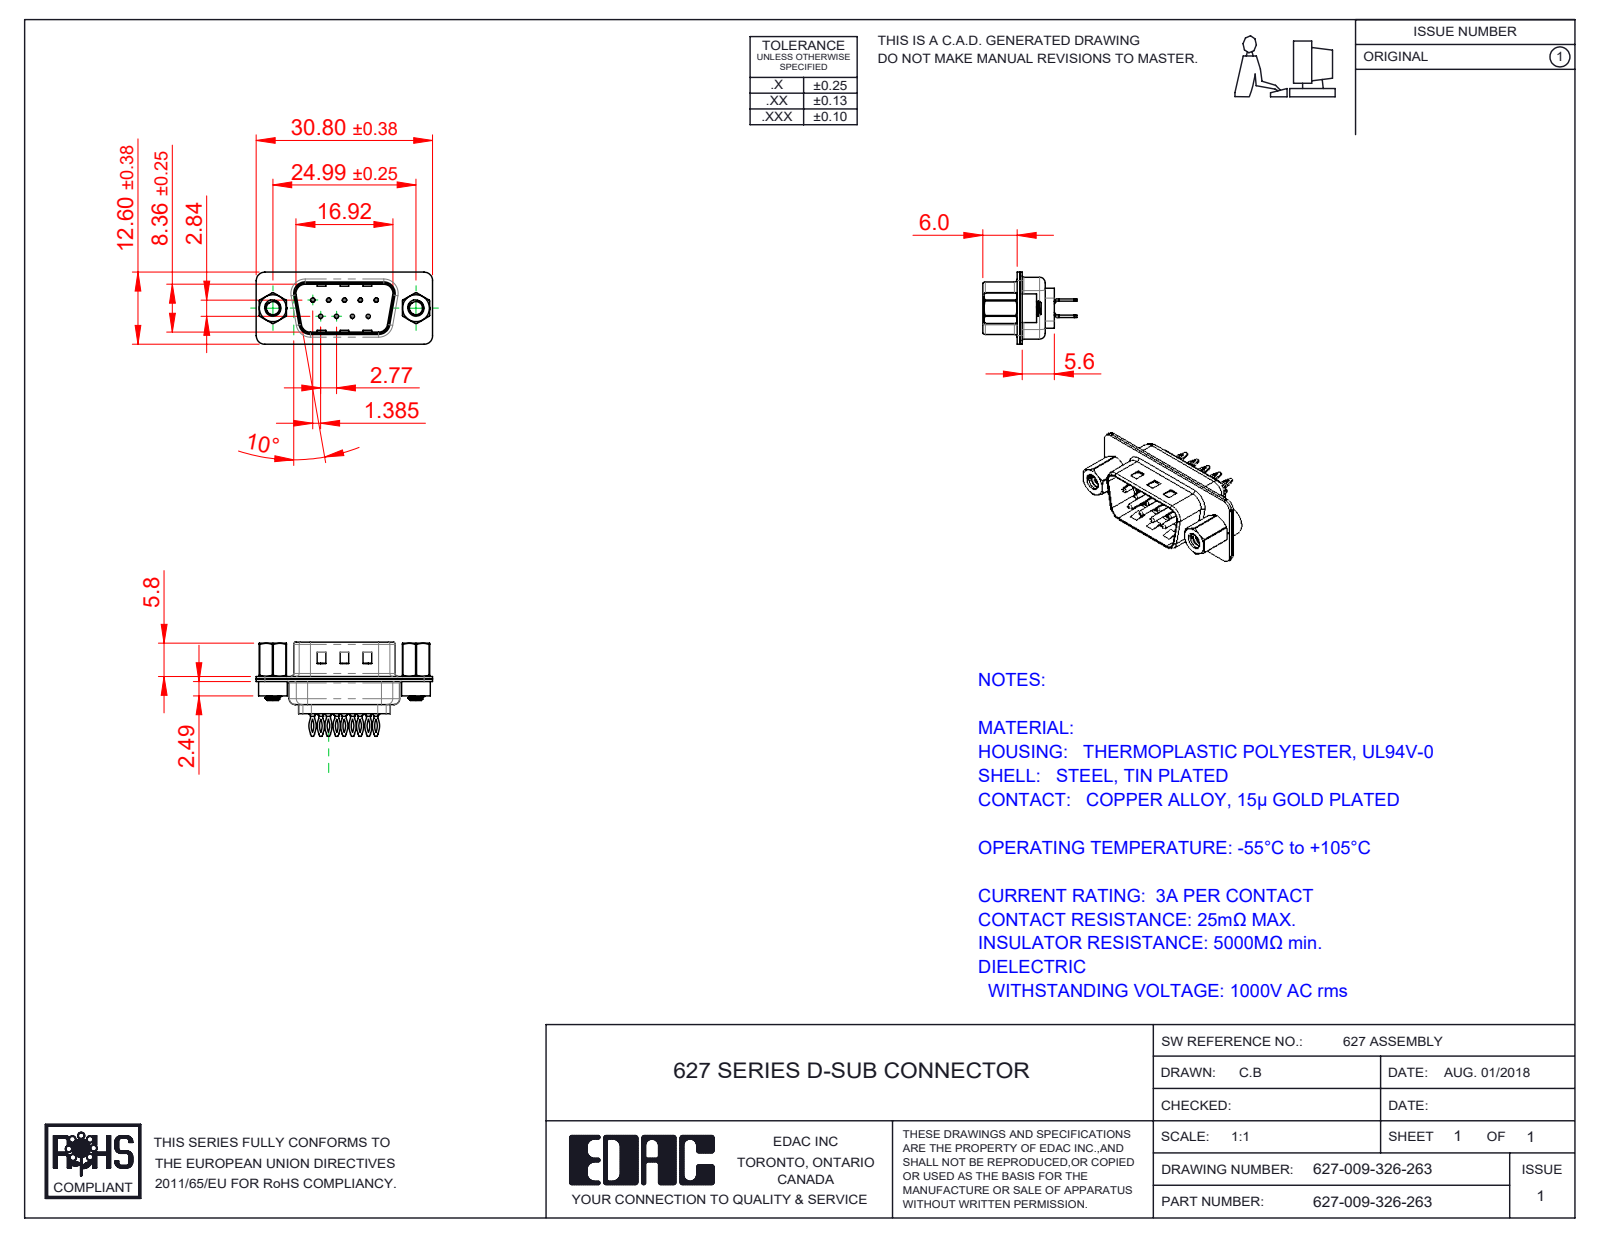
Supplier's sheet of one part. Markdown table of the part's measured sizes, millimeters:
| quantity | value |
| --- | --- |
| part name | 627 4-40 Threaded Rivet; 627 Contact Row 2_26L; 627 4-40 Hex Standoff; 627 Shell Front_09 Contacts (+4 more) |
| STEP written by | SolidWorks 2020 (CONFIG_CONTROL_DESIGN) |
| units | millimeters |
| bodies | 16 solids, 1110 faces (309 planar, 478 cylindrical, 323 other) |
| overall size | 30.8 × 16.45 × 12.6 |
| volume | 1 519 mm³ |
| surface area | 4 378 mm² |
| round holes (diameter × count) | 0.35 × 9, 1.1 × 9, 1.6 × 9, 2.26 × 2, 2.29 × 2, 4 × 2, 4.8 × 2 |
| round bosses / shafts (diameter × count) | 2 × 9, 1.5 × 9, 0.75 × 9, 5 × 2, 4.9 × 2, 2.79 × 2 |
| partial cylindrical surfaces (radius × count) | 1.5 × 18, 2.92 × 18, 3.33 × 18, 2 × 12, 0.5 × 8, 1.6 × 8, 0.25 × 4, 0.6 × 4 |
| main face-to-face distances | 0.45, 0.4, 0.9, 0.82, 9.58, 1.4, 8.76, 0.5, 1.5, 6.05 |
| hole center spacings | 3.16, 2.77, 5.54, 5.03, 5.04, 8.31, 7.48, 7.49 |
